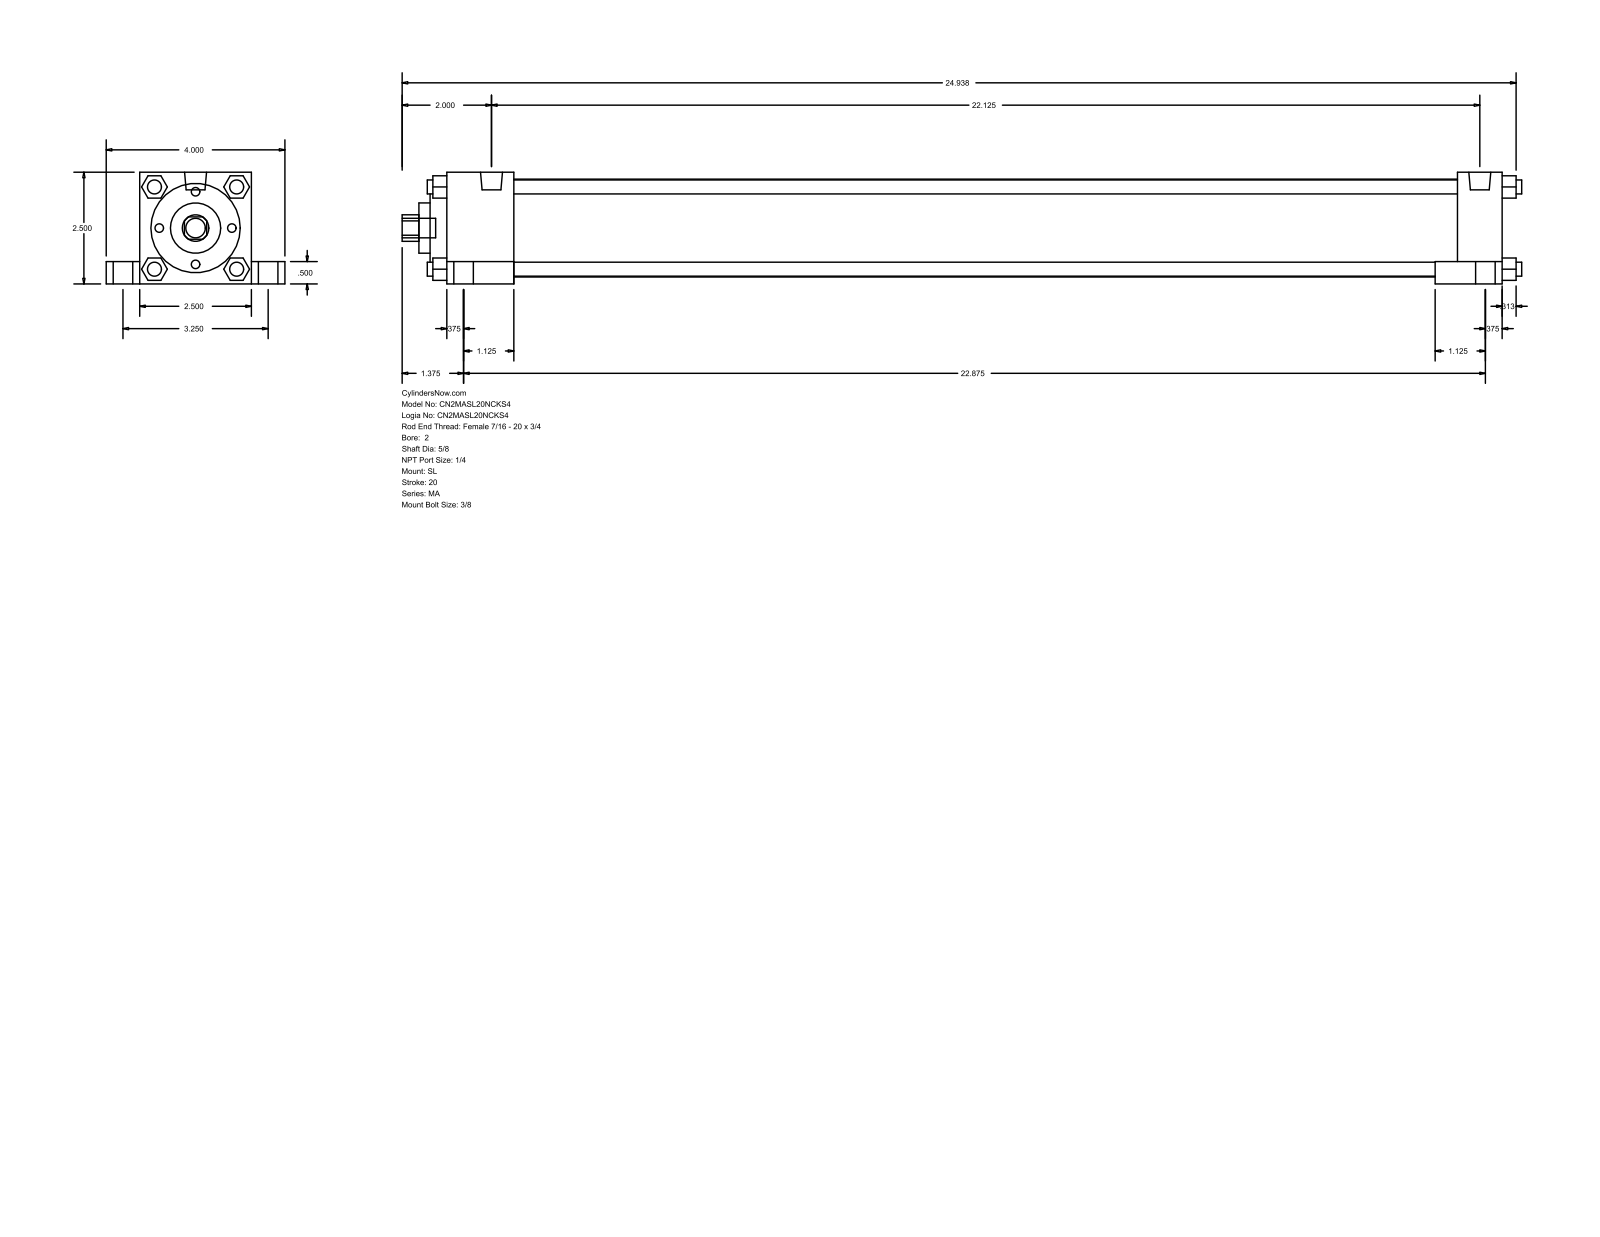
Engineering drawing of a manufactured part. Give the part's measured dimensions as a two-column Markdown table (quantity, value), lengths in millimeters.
| quantity | value |
| --- | --- |
| part name | MA_SL__0200_0.625 |
| STEP written by | GSSL Pune (CONFIG_CONTROL_DESIGN) |
| units | millimeters |
| bodies | 0 solids, 150 faces (113 planar, 37 cylindrical, 0 other) |
| overall size | 636.59 × 101.6 × 63.5 |
| round holes (diameter × count) | 15.88 × 1, 28.57 × 1, 50.8 × 1, 55.63 × 1 |
| round bosses / shafts (diameter × count) | 7.94 × 8, 11.11 × 5, 17.46 × 4, 12.49 × 2 |
| partial cylindrical surfaces (radius × count) | 7.54 × 1 |
| main face-to-face distances | 63.5, 12.7, 9.52, 25.4, 19.05, 82.55, 38.1, 600.08, 50.8, 561.98 |
